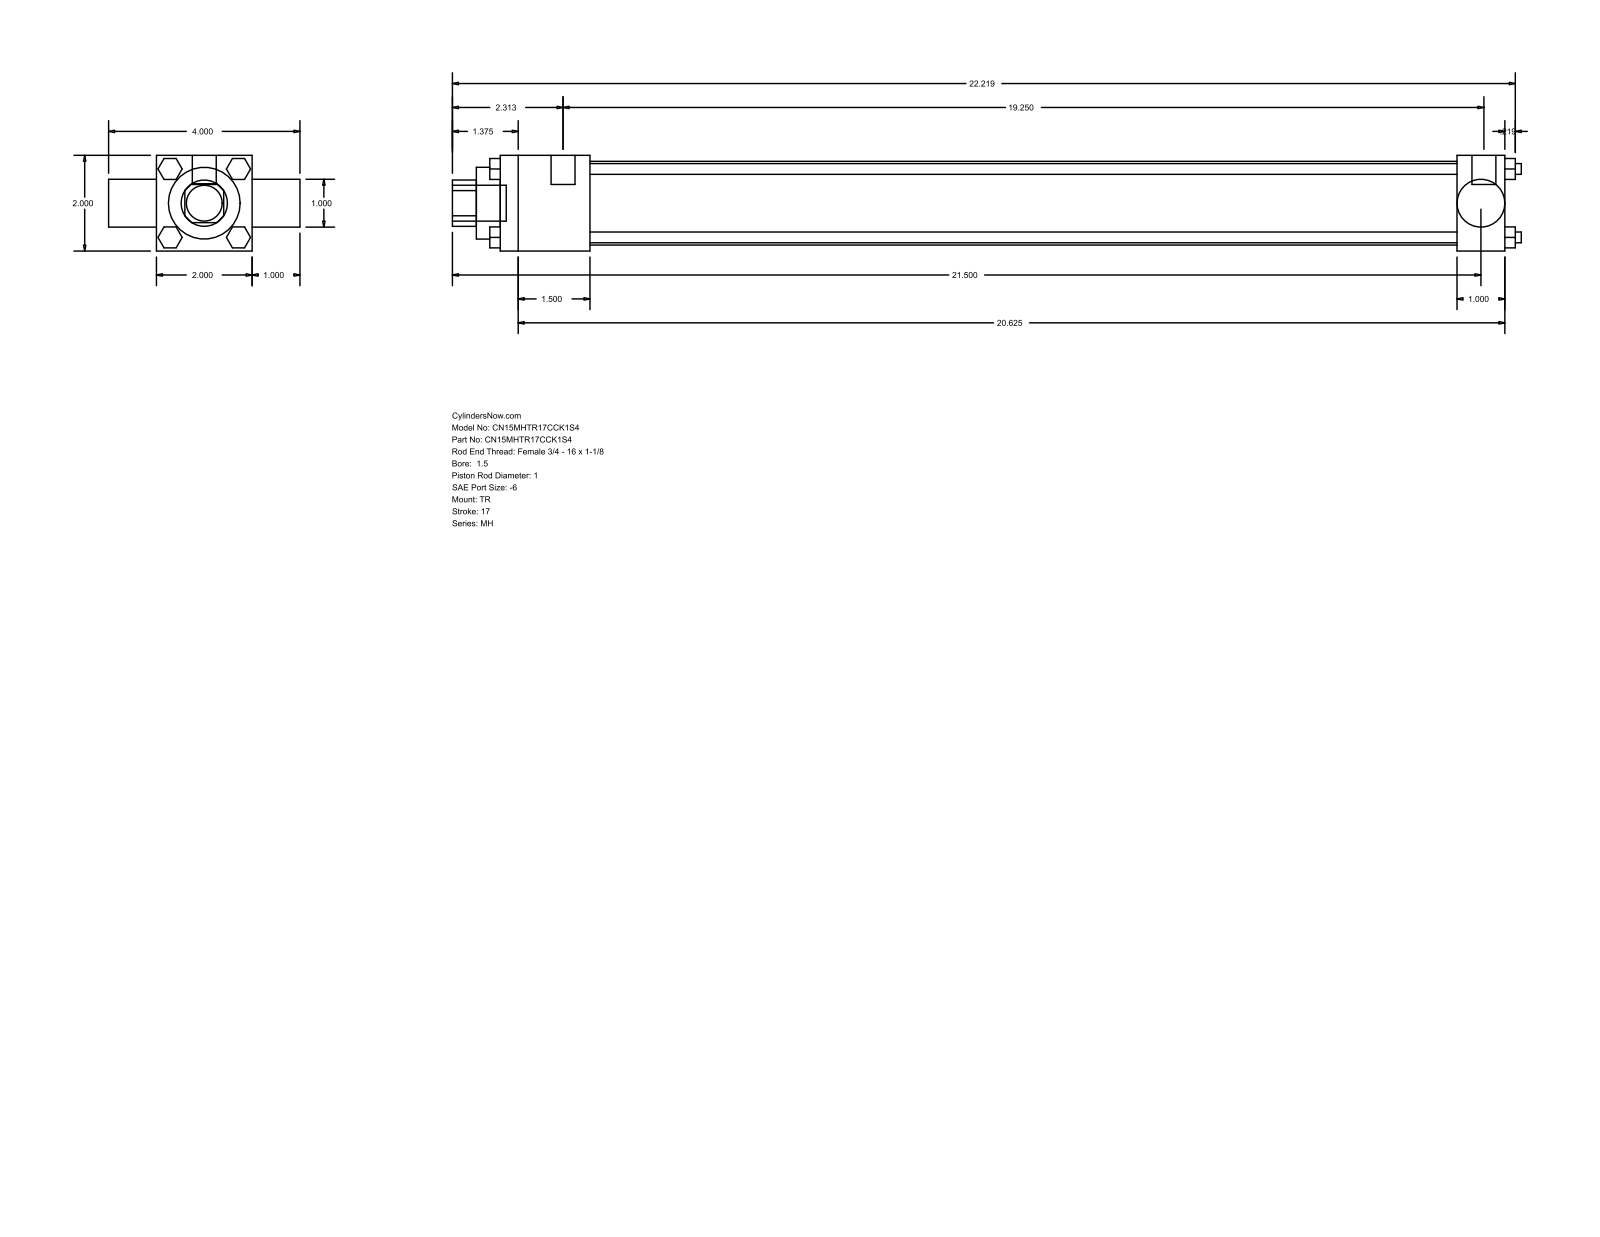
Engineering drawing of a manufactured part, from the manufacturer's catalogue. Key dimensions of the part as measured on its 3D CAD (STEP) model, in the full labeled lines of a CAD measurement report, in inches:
Part name (STEP PRODUCT): MH_TR__0150_1
STEP written by: GSSL Pune (CONFIG_CONTROL_DESIGN)
Units: inches
Bodies: 0 solids, 120 faces (92 planar, 28 cylindrical, 0 other)
Overall size (bounding box): 22.344 × 4 × 2
Round holes (diameter × count): ⌀0.998 ×1, ⌀1 ×1, ⌀1.5 ×1, ⌀1.75 ×1
Round bosses / shafts (diameter × count): ⌀0.225 ×4, ⌀0.219 ×3, ⌀0.5 ×2, ⌀0.75 ×1
Partial cylindrical surfaces — rounded edges, fillets, slot ends (radius × count): R0.484 ×1
Main face-to-face distances: 2, 1, 21, 3, 1.875, 19.125, 20, 18.125, 21.219, 0.5
